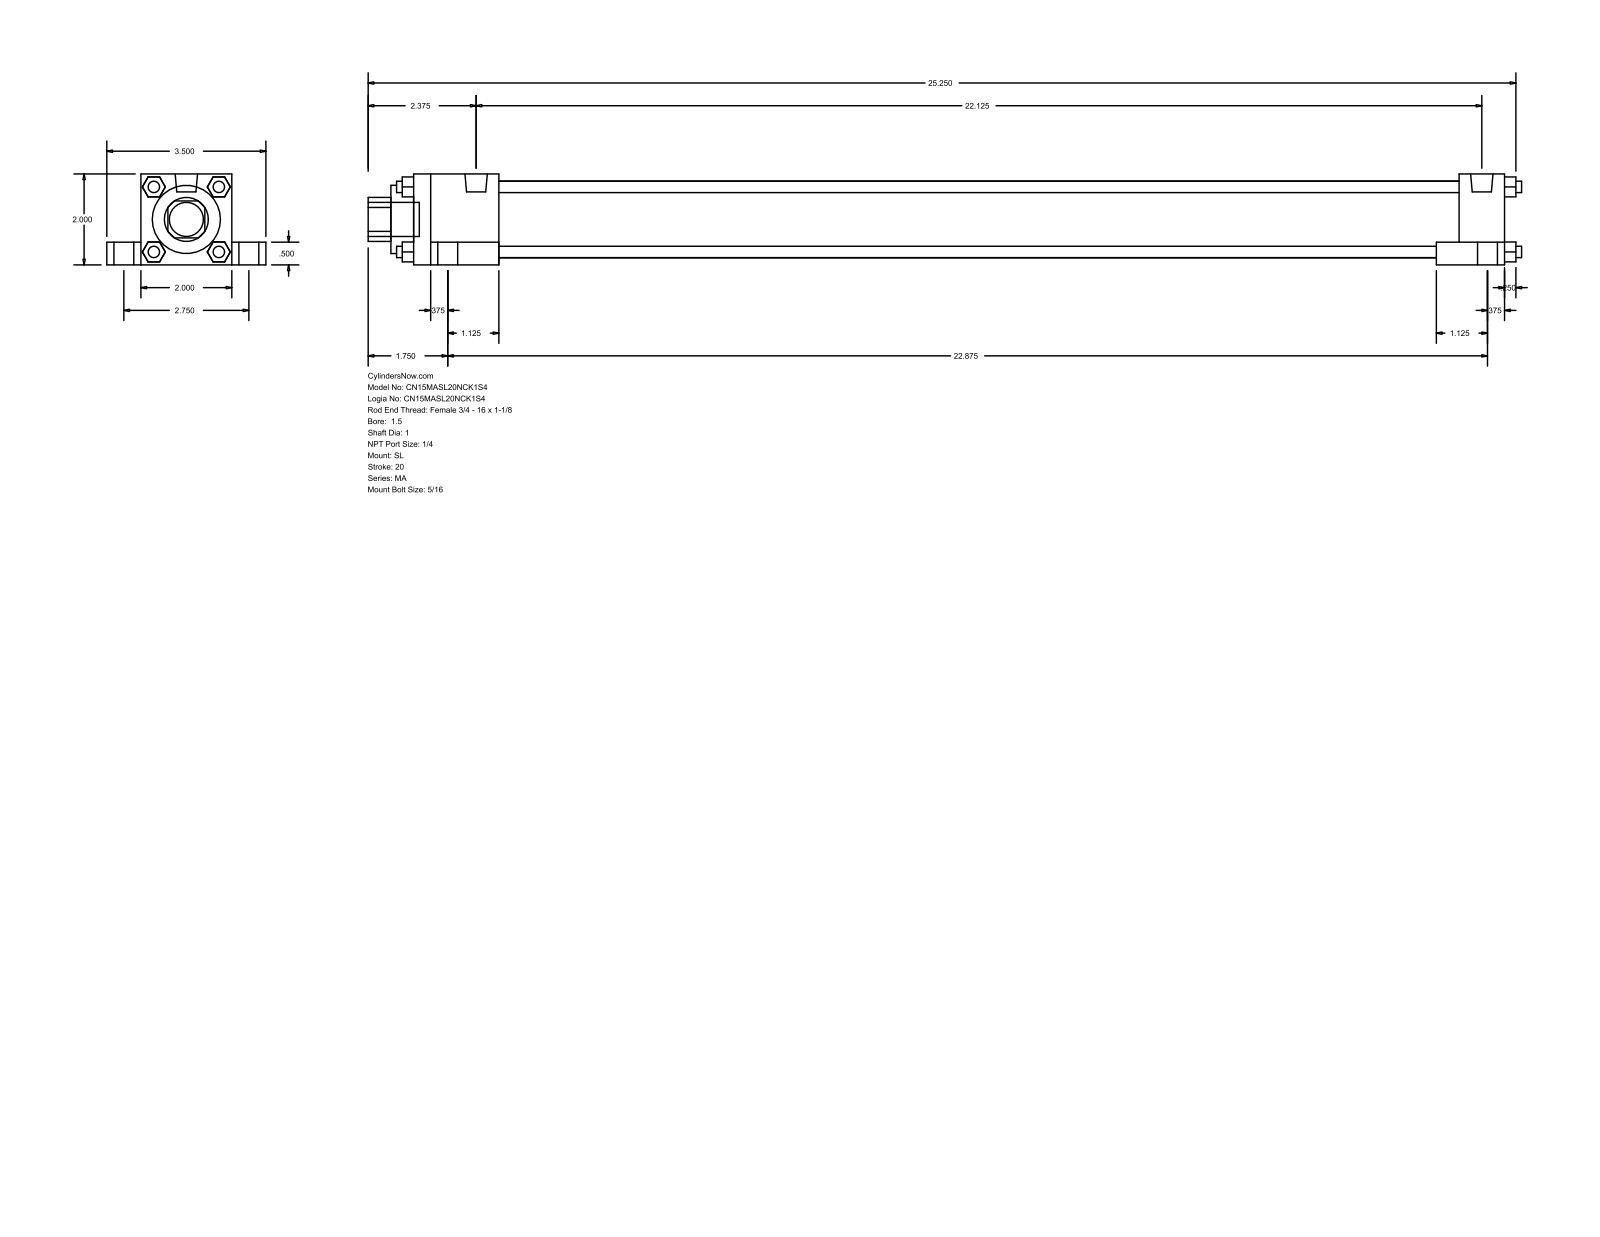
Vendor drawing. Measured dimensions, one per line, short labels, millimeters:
name: MA_SL__0150_1
written by: GSSL Pune (CONFIG_CONTROL_DESIGN)
unit: mm
bodies: 0 solids, 148 faces (112 planar, 36 cylindrical, 0 other)
size: 644.52 × 88.9 × 50.8
holes: 1× ⌀25.4, 1× ⌀38.1, 1× ⌀42.93
bosses: 4× ⌀17.46, 4× ⌀11.11, 4× ⌀7.94, 4× ⌀6.35, 2× ⌀12.49, 1× ⌀19.05
rounds: 1× R12.29
face distances: 50.8, 12.7, 19.05, 9.52, 69.85, 38.1, 6.35, 609.6, 25.4, 584.2
